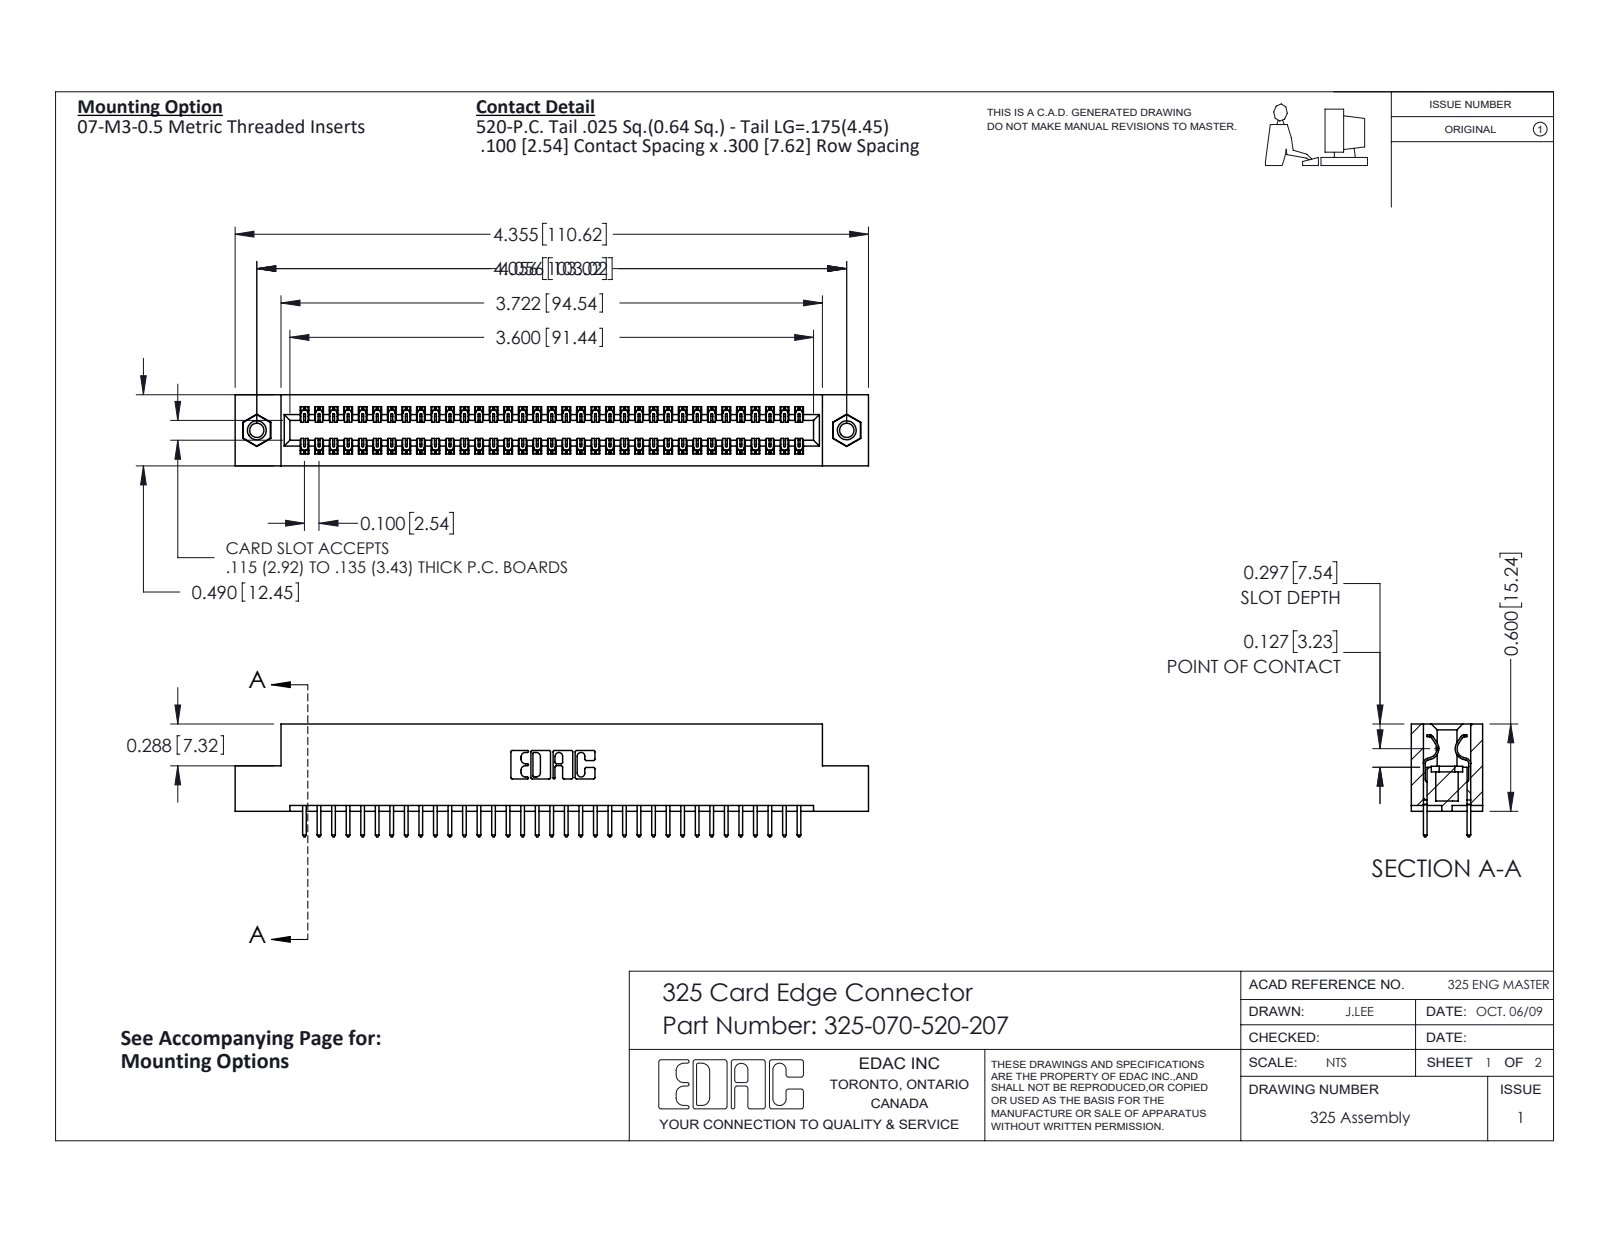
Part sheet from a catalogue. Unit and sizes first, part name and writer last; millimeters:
Units: millimetres
Overall size (bounding box): 110.6 × 19.7 × 12.4
Round holes (diameter × count): ⌀2.5 ×2, ⌀3.2 ×2, ⌀4.1 ×2
Round bosses / shafts (diameter × count): ⌀3.9 ×2
Partial cylindrical surfaces — rounded edges, fillets, slot ends (radius × count): R0.2 ×105, R0.3 ×70, R0.3 ×22, R0.2 ×6, R0.8 ×6, R0.7 ×3, R0.4 ×2, R0.6 ×2
Main face-to-face distances: 2.1, 10.3, 12.4, 7.6, 2.7, 9.7, 0.6, 8.3, 7, 14.2
Hole centre spacings: 103
Volume: 14 200 mm³ · Surface area: 16 900 mm²
Bodies: 73 solids, 3814 faces (2622 planar, 1176 cylindrical, 16 other)
Part name (STEP PRODUCT): 325 Part_TI; 345-250-001_345-250-005-103; 325-070-520-207; 325-292-001_325-293-120
STEP written by: SolidWorks 2016 (CONFIG_CONTROL_DESIGN)
